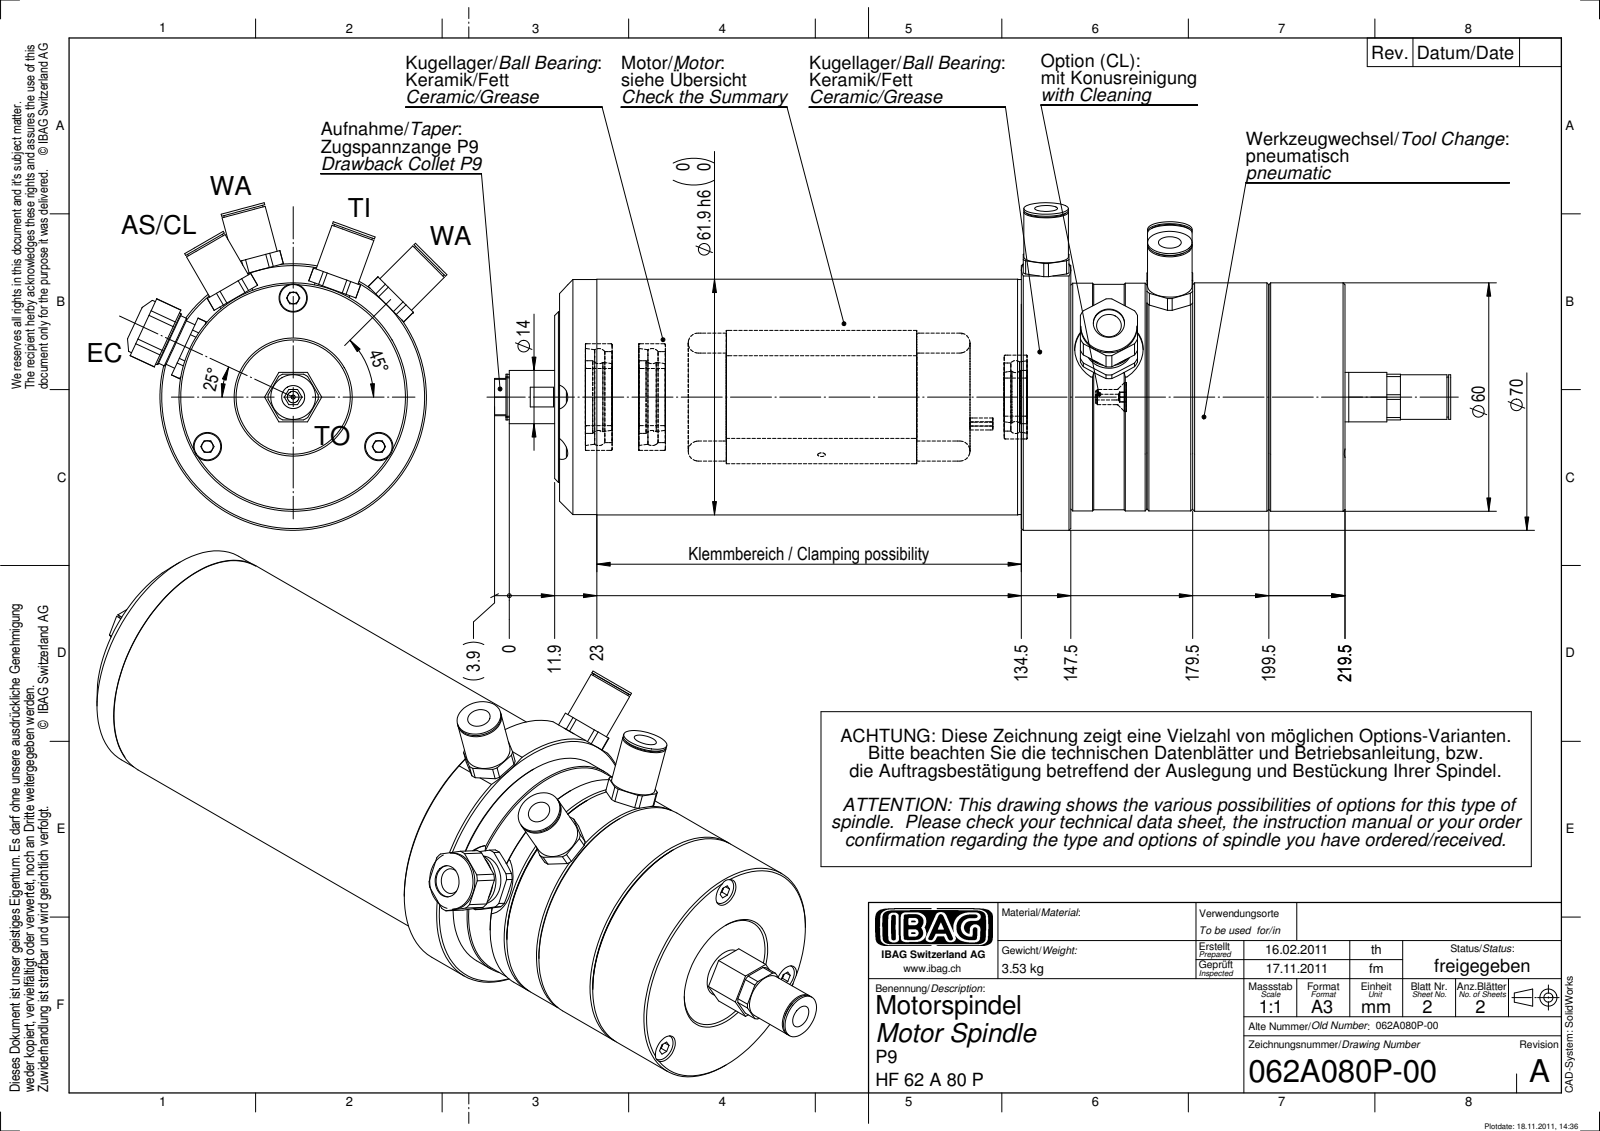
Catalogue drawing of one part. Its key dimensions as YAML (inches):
part_name: "062A080P-00A"
step_written_by: "SolidWorks 2010 (CONFIG_CONTROL_DESIGN)"
units: inches
bodies: {solids: 0, faces: 516, planar: 222, cylindrical: 182, other: 112}
overall_size: [9.888, 3.387, 3.303]
round_holes:
  - {diameter: 0.256, count: 7}
  - {diameter: 0.236, count: 5}
  - {diameter: 0.291, count: 3}
  - {diameter: 0.13, count: 1}
  - {diameter: 0.197, count: 1}
  - {diameter: 0.323, count: 1}
  - {diameter: 0.567, count: 1}
round_bosses_or_shafts:
  - {diameter: 0.217, count: 6}
  - {diameter: 0.461, count: 5}
  - {diameter: 0.415, count: 5}
  - {diameter: 0.224, count: 4}
  - {diameter: 0.383, count: 2}
  - {diameter: 2.756, count: 1}
  - {diameter: 2.437, count: 1}
  - {diameter: 2.429, count: 1}
partial_cylinders:
  - {radius: 0.26, count: 5}
  - {radius: 0.325, count: 2}
  - {radius: 0.354, count: 1}
face_to_face_distances: [0.787, 2.047, 1.26, 2.835, 0.472, 5.339, 6.126, 7.386, 8.173, 6.598]
hole_center_spacings: [1.781, 1.033, 1.79, 0.532, 1.773, 1.996, 0.535, 1.024]
